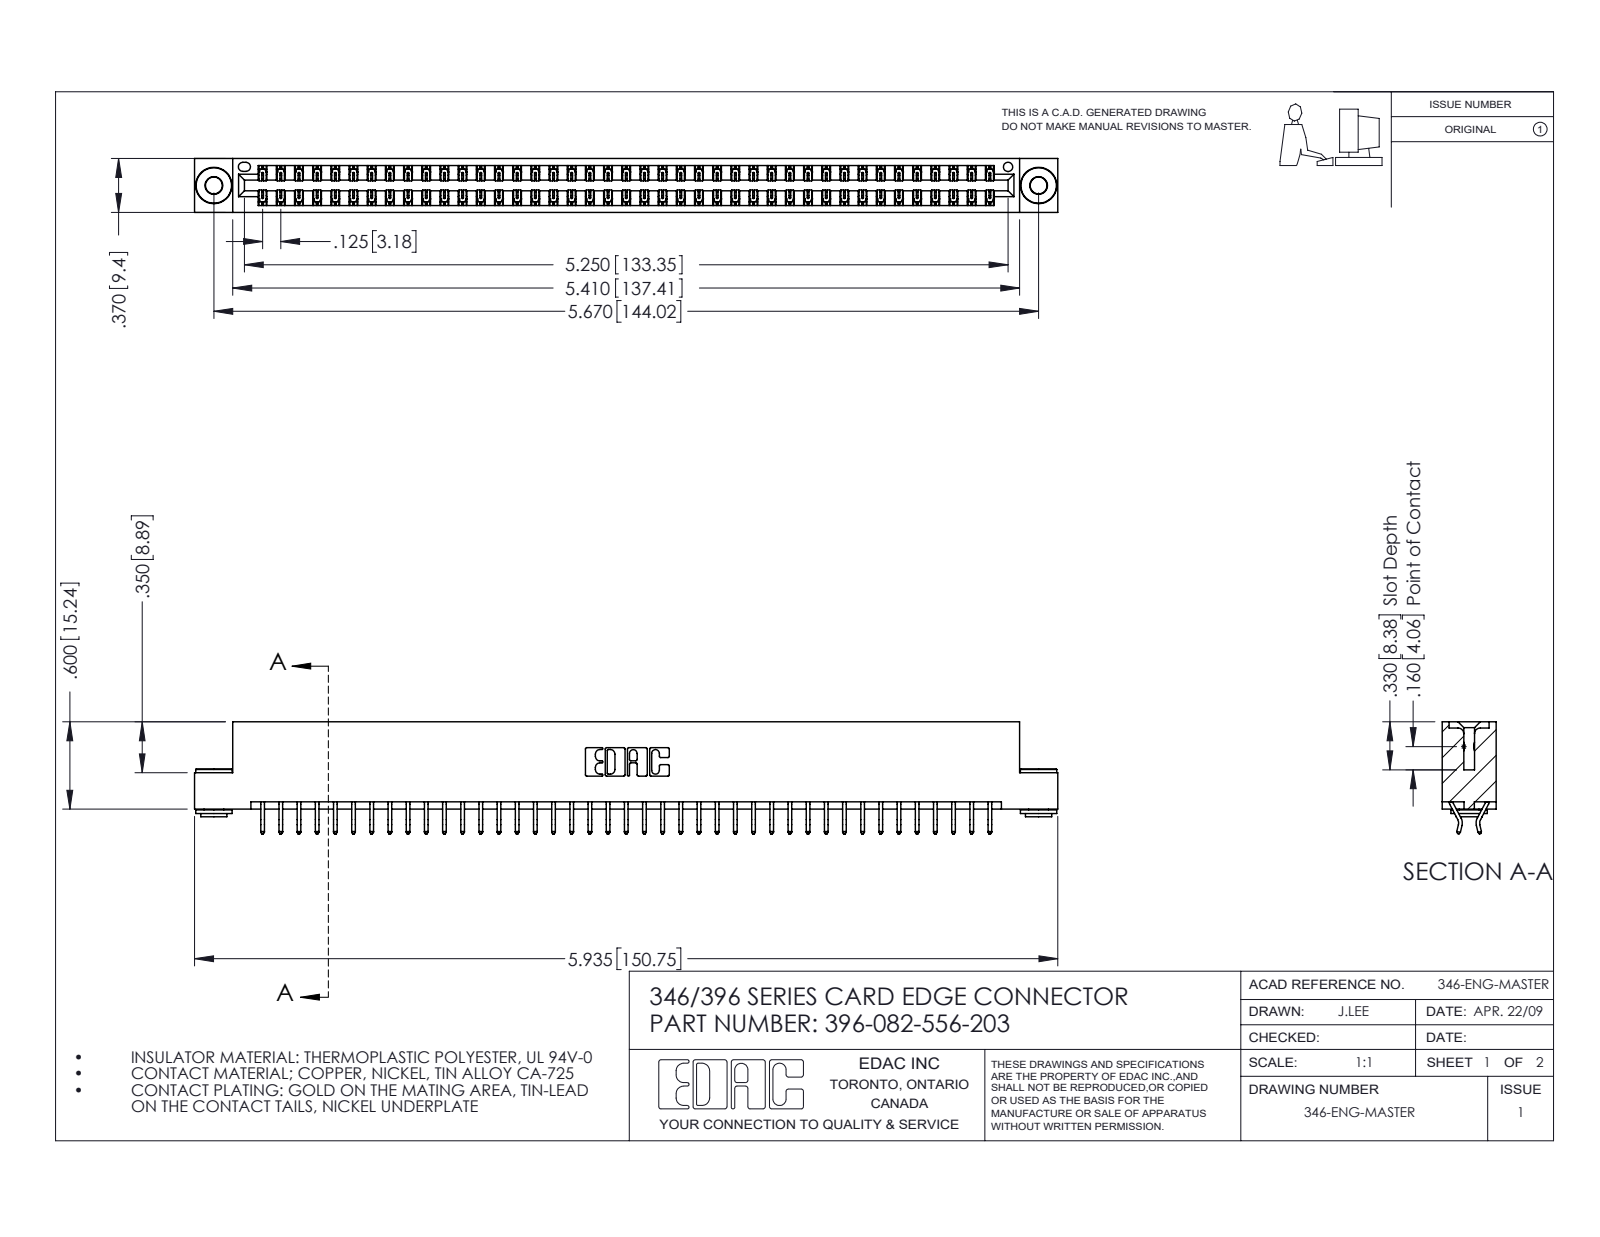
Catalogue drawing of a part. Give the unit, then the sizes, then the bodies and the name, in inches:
Units: inches
Overall size (bounding box): 5.935 × 0.77 × 0.37
Round holes (diameter × count): ⌀0.116 ×2, ⌀0.156 ×2, ⌀0.064 ×1
Round bosses / shafts (diameter × count): ⌀0.25 ×2, ⌀0.18 ×2, ⌀0.136 ×2
Partial cylindrical surfaces — rounded edges, fillets, slot ends (radius × count): R0.006 ×123, R0.01 ×22, R0.007 ×6, R0.031 ×6, R0.026 ×3, R0.01 ×2, R0.014 ×2, R0.022 ×2
Main face-to-face distances: 0.048, 0.322, 0.37, 0.25, 0.025, 0.072, 0.298, 0.275, 0.148, 0.222
Hole centre spacings: 0.246, 5.461, 5.67
Volume: 0.898 in³ · Surface area: 31.53 in²
Bodies: 85 solids, 4916 faces (3284 planar, 1624 cylindrical, 8 other)
Part name (STEP PRODUCT): 396-082-556-203; 345-292-001_556 Tail; 346 Part_Flush Mounting Lugs - 0.156 Dia-TH; 345-250-002_345-250-002-102
STEP written by: SolidWorks 2016 (CONFIG_CONTROL_DESIGN)
